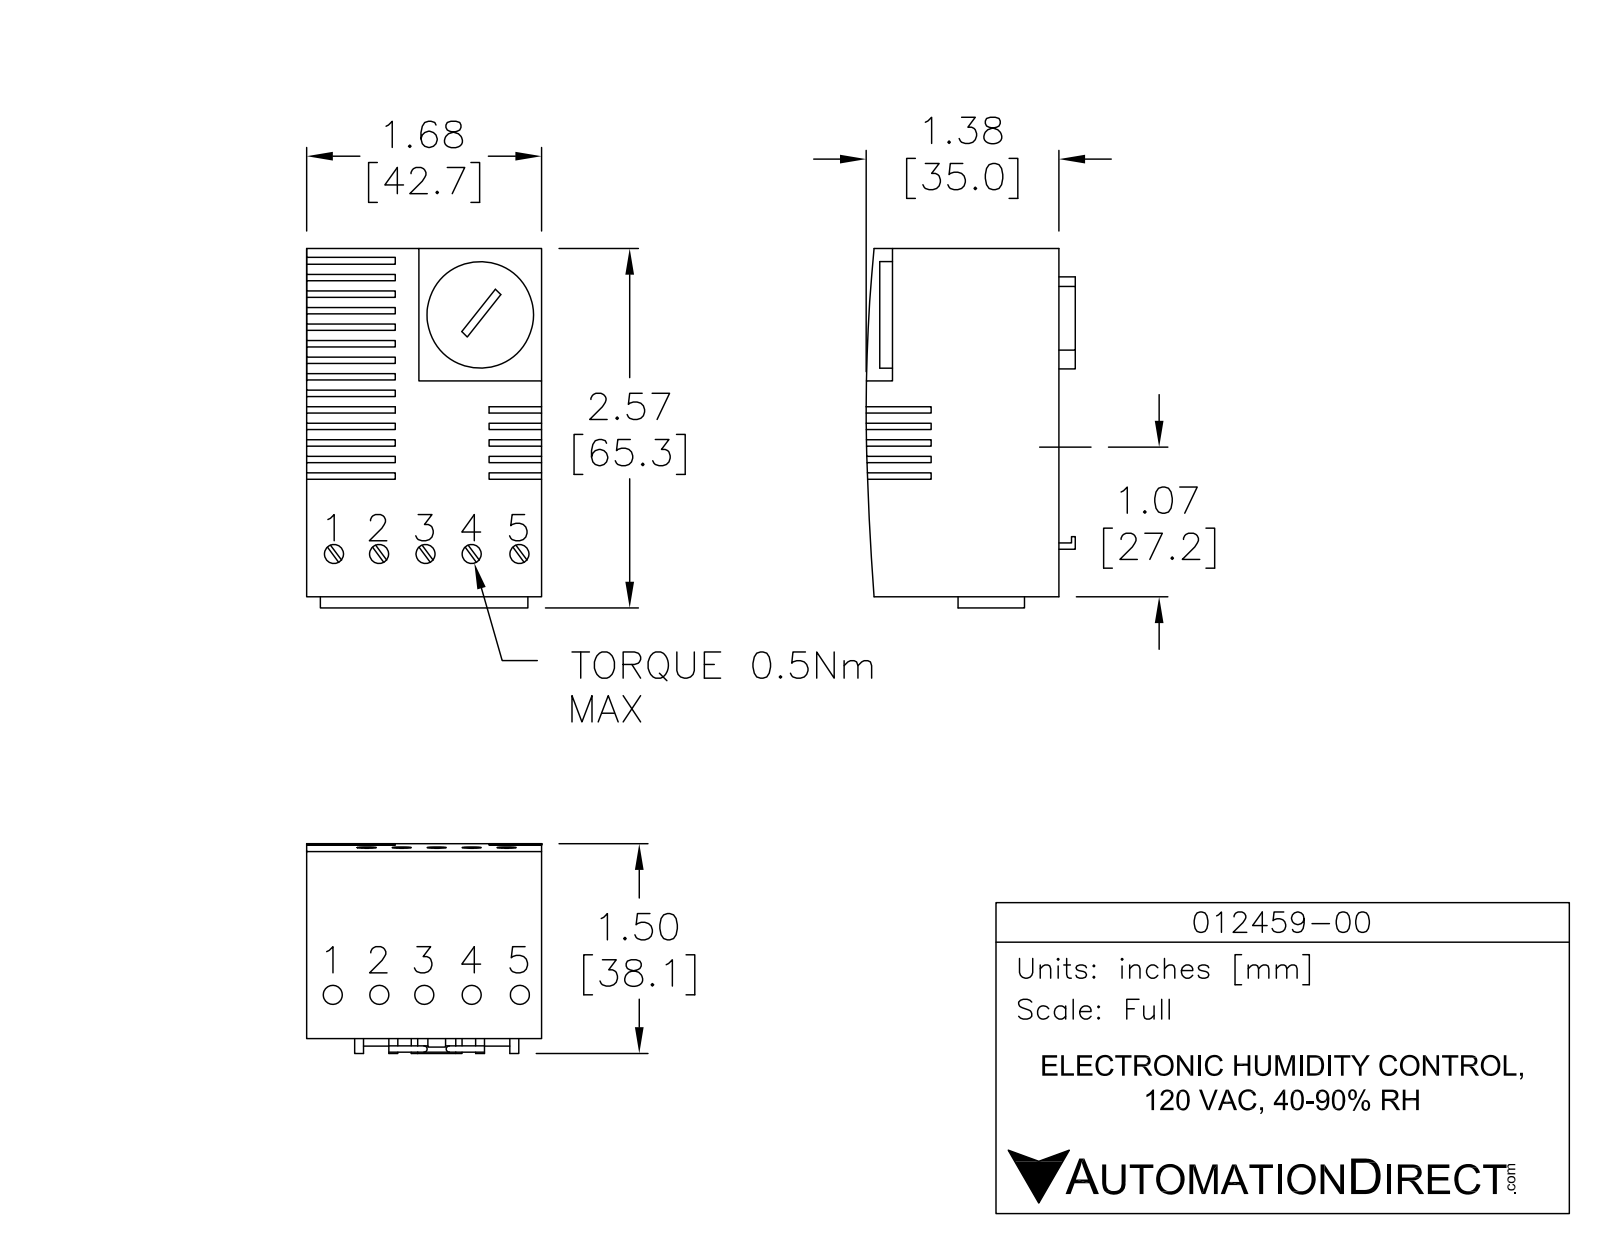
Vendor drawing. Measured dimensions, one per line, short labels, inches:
name: 012459-00
written by: SolidWorks 2013 (AUTOMOTIVE_DESIGN)
unit: in
bodies: 1 solid, 392 faces (154 planar, 138 cylindrical, 100 other)
size: 2.575 × 1.685 × 1.5
volume: 5.02 in³; area: 29.27 in²
holes: 10× ⌀0.15, 1× ⌀0.59
rounds: 66× R0.027, 11× R0.06, 10× R0.03, 5× R0.028, 1× R0.02, 1× R0.15, 1× R12.549, 1× R12.94
face distances: 0.12, 1.685, 0.24, 2.5, 0.055, 0.785, 1.2, 0.065, 0.185, 0.24
hole spacings: 0.3, 0.6, 0.9, 1.2, 1.676, 1.697, 1.708, 1.791
